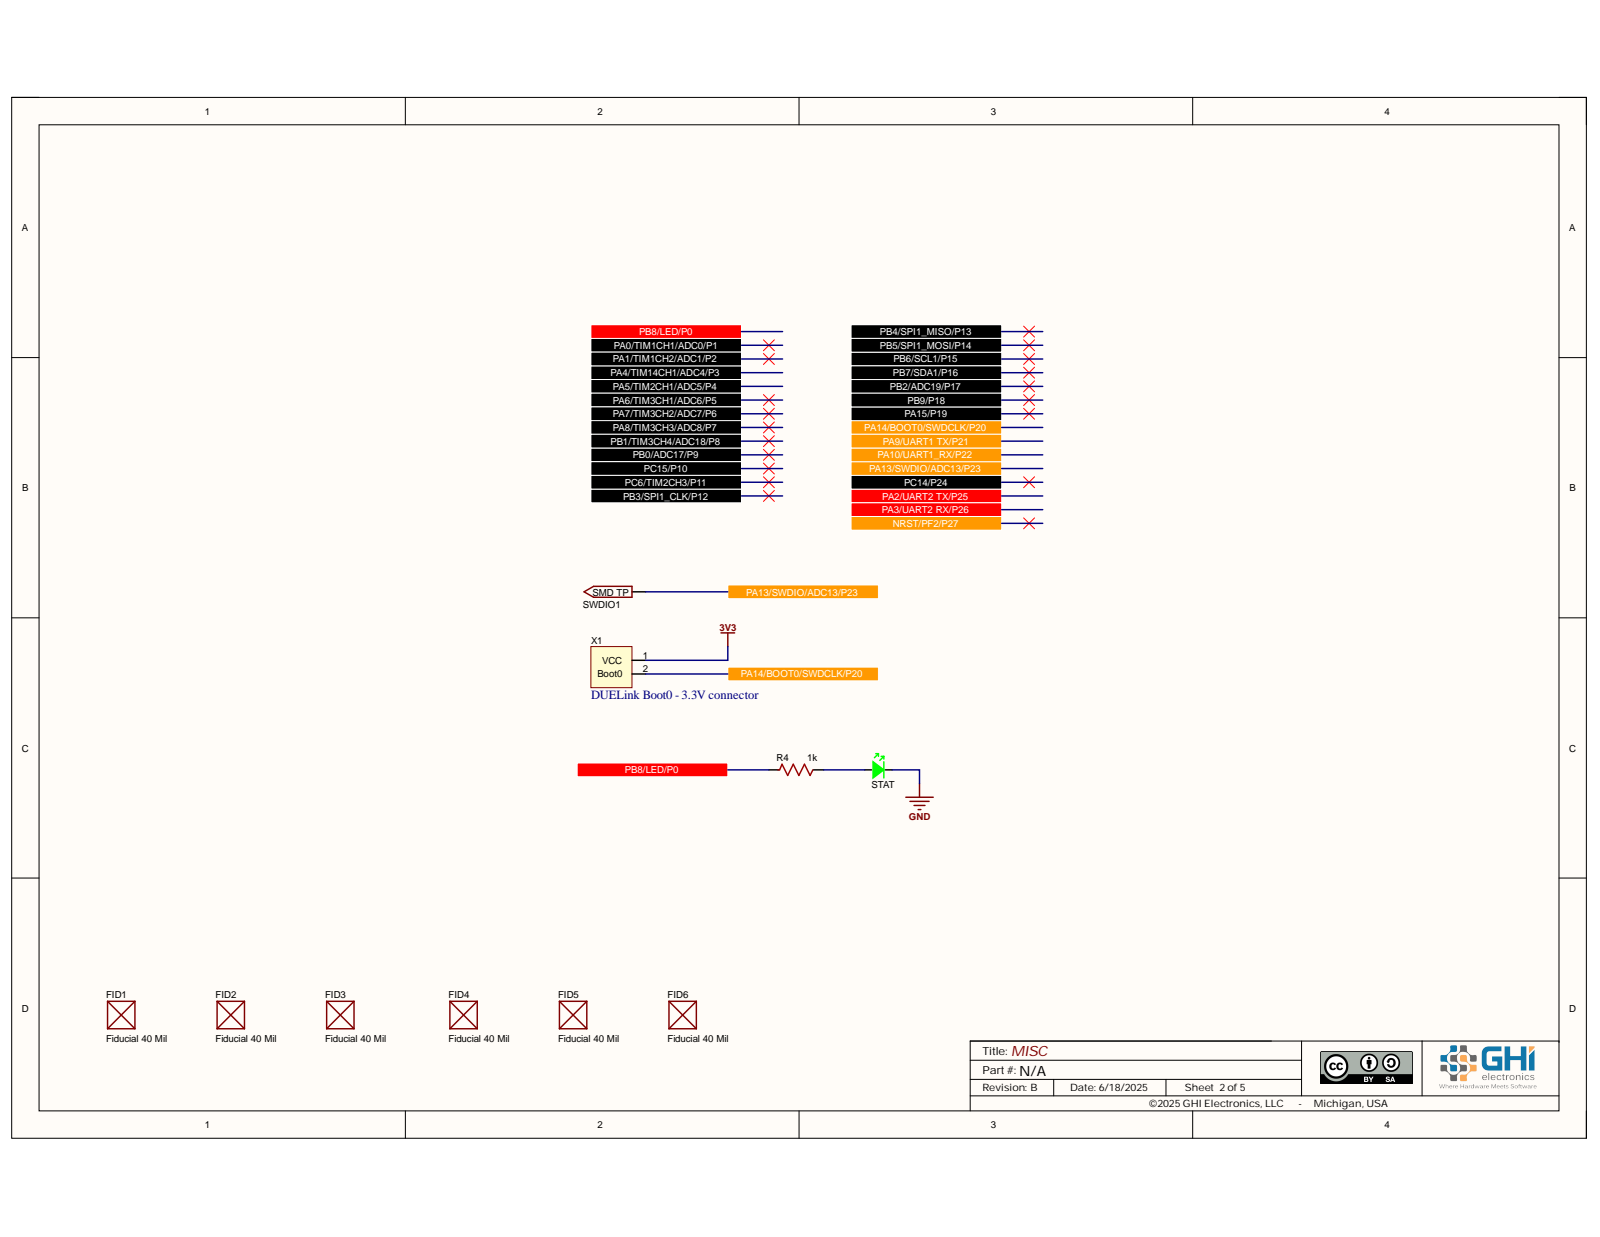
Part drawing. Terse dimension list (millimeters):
name: PCB; Board; J11; Conn_Harwin_M20-9990445_eec (+7 more)
written by: Open CASCADE 7.5 (AUTOMOTIVE_DESIGN)
unit: mm
bodies: 250 solids, 4751 faces (4152 planar, 479 cylindrical, 120 other)
size: 45 × 33.1 × 25.57
volume: 4 066 mm³; area: 9 267 mm²
holes: 10× ⌀1.6, 4× ⌀1.02, 4× ⌀1.82, 4× ⌀2, 3× ⌀0.6, 2× ⌀1.02, 2× ⌀3, 2× ⌀12.32, 2× ⌀13
bosses: 4× ⌀13, 4× ⌀2.53, 2× ⌀16, 2× ⌀9
rounds: 35× R0.12, 14× R0.15, 4× R0.16, 4× R0.17, 4× R0.24, 2× R0.17, 2× R0.18, 2× R0.18
face distances: 1, 1.2, 8, 7, 6.8, 8.5, 9, 5, 0.5, 2.2
hole spacings: 2.54, 35.04, 26, 26.48, 5, 5.08, 11.69, 17
